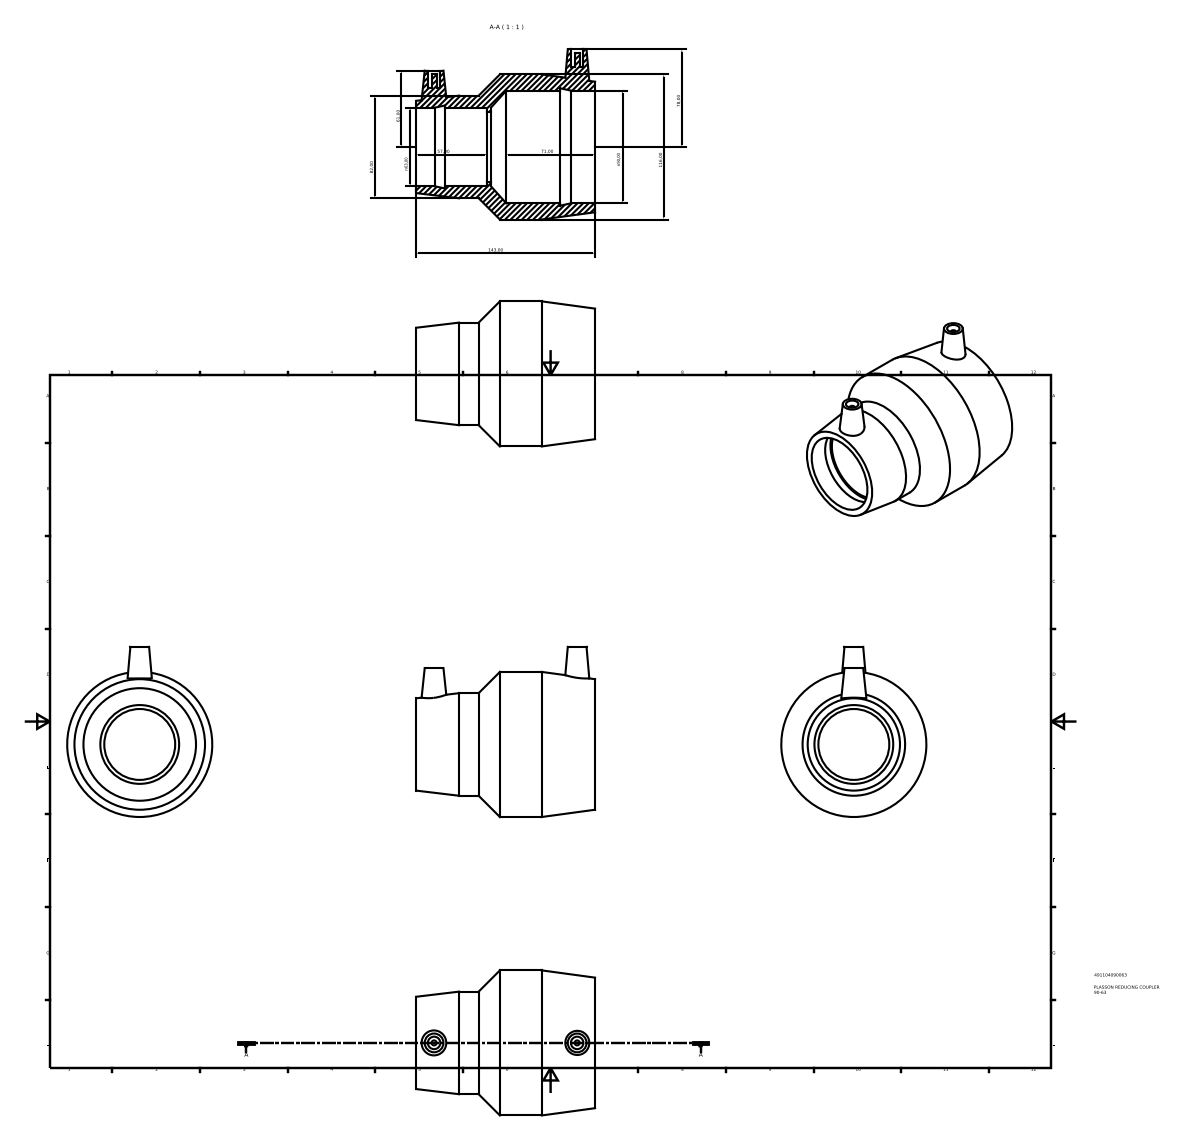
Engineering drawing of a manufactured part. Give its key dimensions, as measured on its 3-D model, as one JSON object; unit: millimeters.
{"part_name": "491104090063", "step_written_by": "Autodesk Inventor 2015 (AUTOMOTIVE_DESIGN)", "units": "millimeters", "bodies": {"solids": 1, "faces": 31, "planar": 12, "cylindrical": 11, "other": 8}, "overall_size": [143, 136, 116], "volume_mm3": 450922, "surface_area_mm2": 92399, "round_holes": [[10, 2], [56.7, 1], [63, 1], [90, 1]], "round_bosses_or_shafts": [[4, 2], [116, 1], [82, 1]], "face_to_face_distances": [143, 59.85, 83.15, 57, 2.85, 86, 114.6, 57.6, 54.75, 28.4], "hole_center_spacings": [114.4]}
